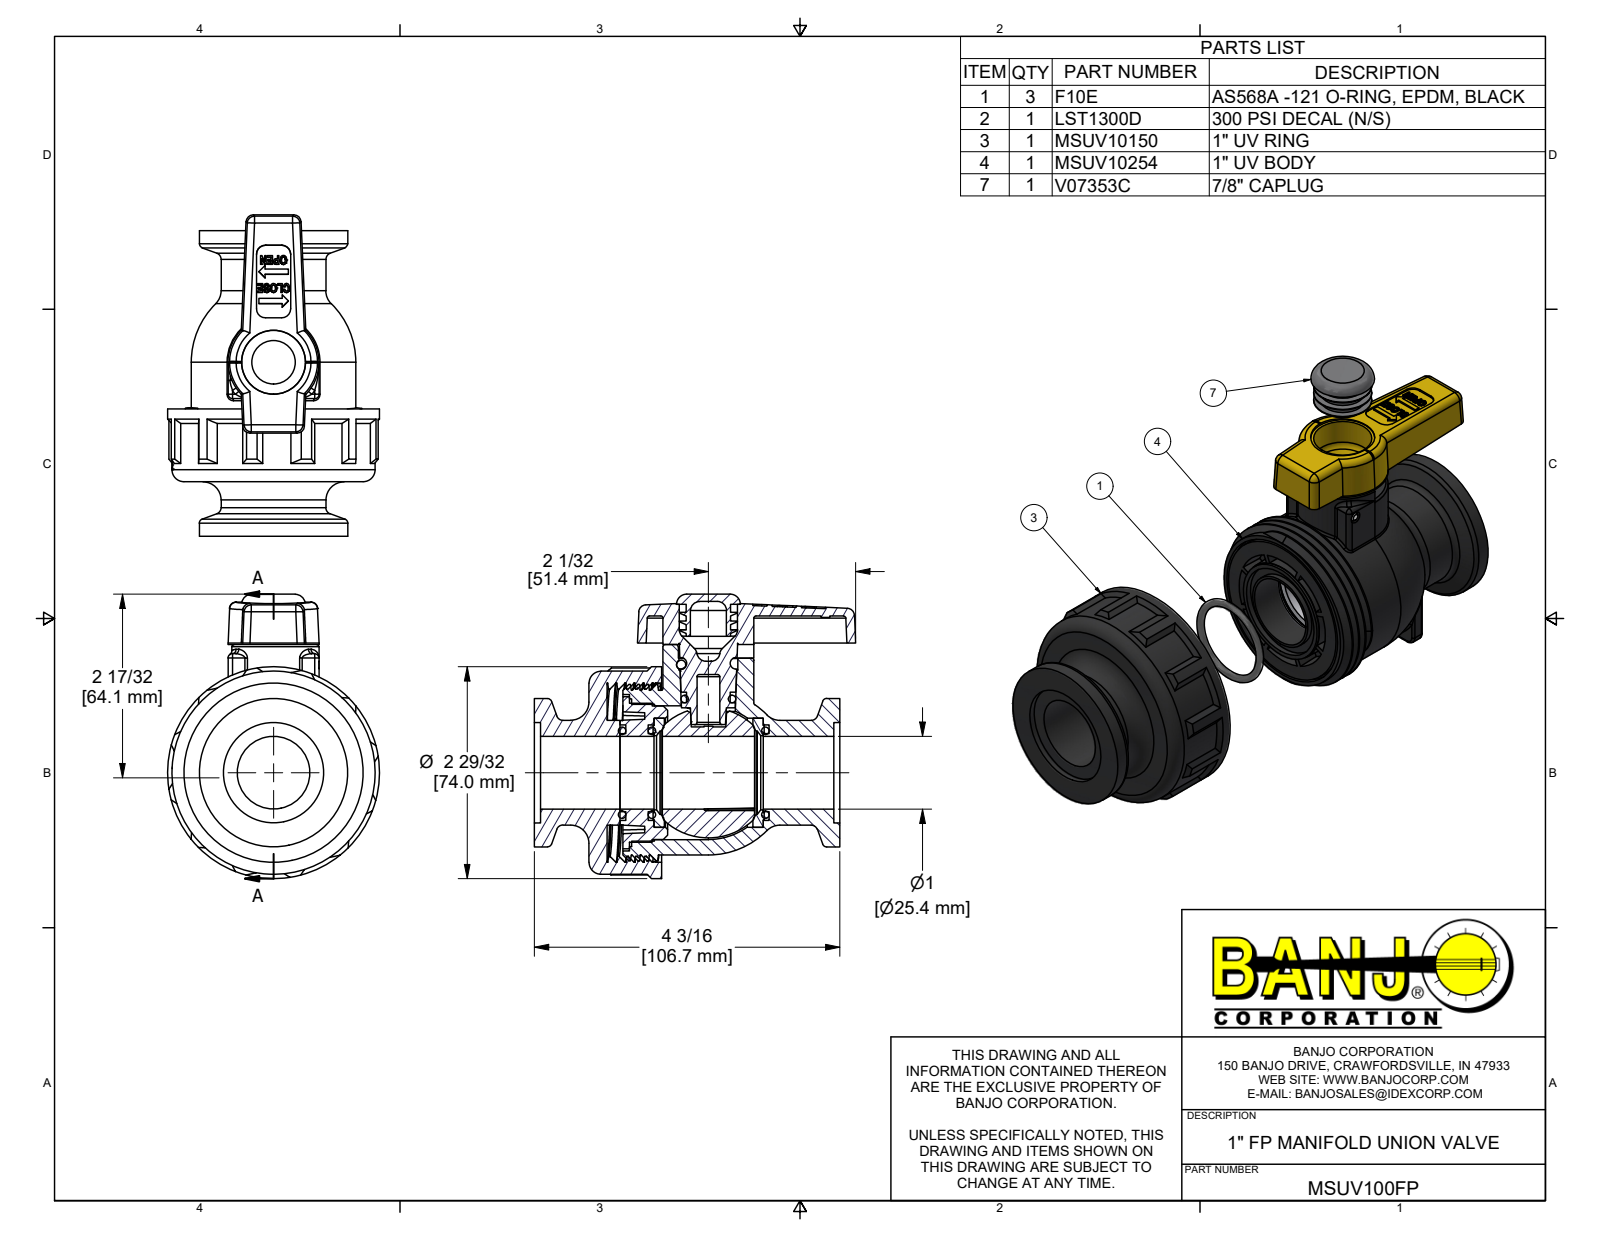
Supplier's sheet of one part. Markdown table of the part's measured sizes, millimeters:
| quantity | value |
| --- | --- |
| part name | MSUV100FP; MSUV10254; UV10257; V10258B (+8 more) |
| STEP written by | Autodesk Inventor 2022 (AUTOMOTIVE_DESIGN) |
| units | millimeters |
| bodies | 13 solids, 865 faces (384 planar, 159 cylindrical, 322 other) |
| overall size | 112.2 × 99.3 × 74 |
| volume | 202 400 mm³ |
| surface area | 94 450 mm² |
| round holes (diameter × count) | 8 × 1, 12.5 × 1, 20.4 × 1, 20.6 × 1, 22.4 × 1, 25.4 × 1, 25.9 × 1, 27.8 × 1, 33.4 × 1, 35.1 × 1, 38.1 × 1, 46.7 × 1 |
| round bosses / shafts (diameter × count) | 74 × 1, 70.9 × 1, 61.7 × 1, 57.5 × 1, 53.1 × 1, 51.8 × 1, 48.5 × 1, 46.6 × 1 |
| partial cylindrical surfaces (radius × count) | 0.8 × 15, 2.5 × 10, 1.5 × 8, 3.2 × 6, 16.5 × 4, 17.8 × 2, 9.4 × 1, 9.6 × 1 |
| main face-to-face distances | 19.1, 25.4, 13.5, 6.4, 7.8, 44.5, 106.7, 87.6, 81.3, 62.2 |
